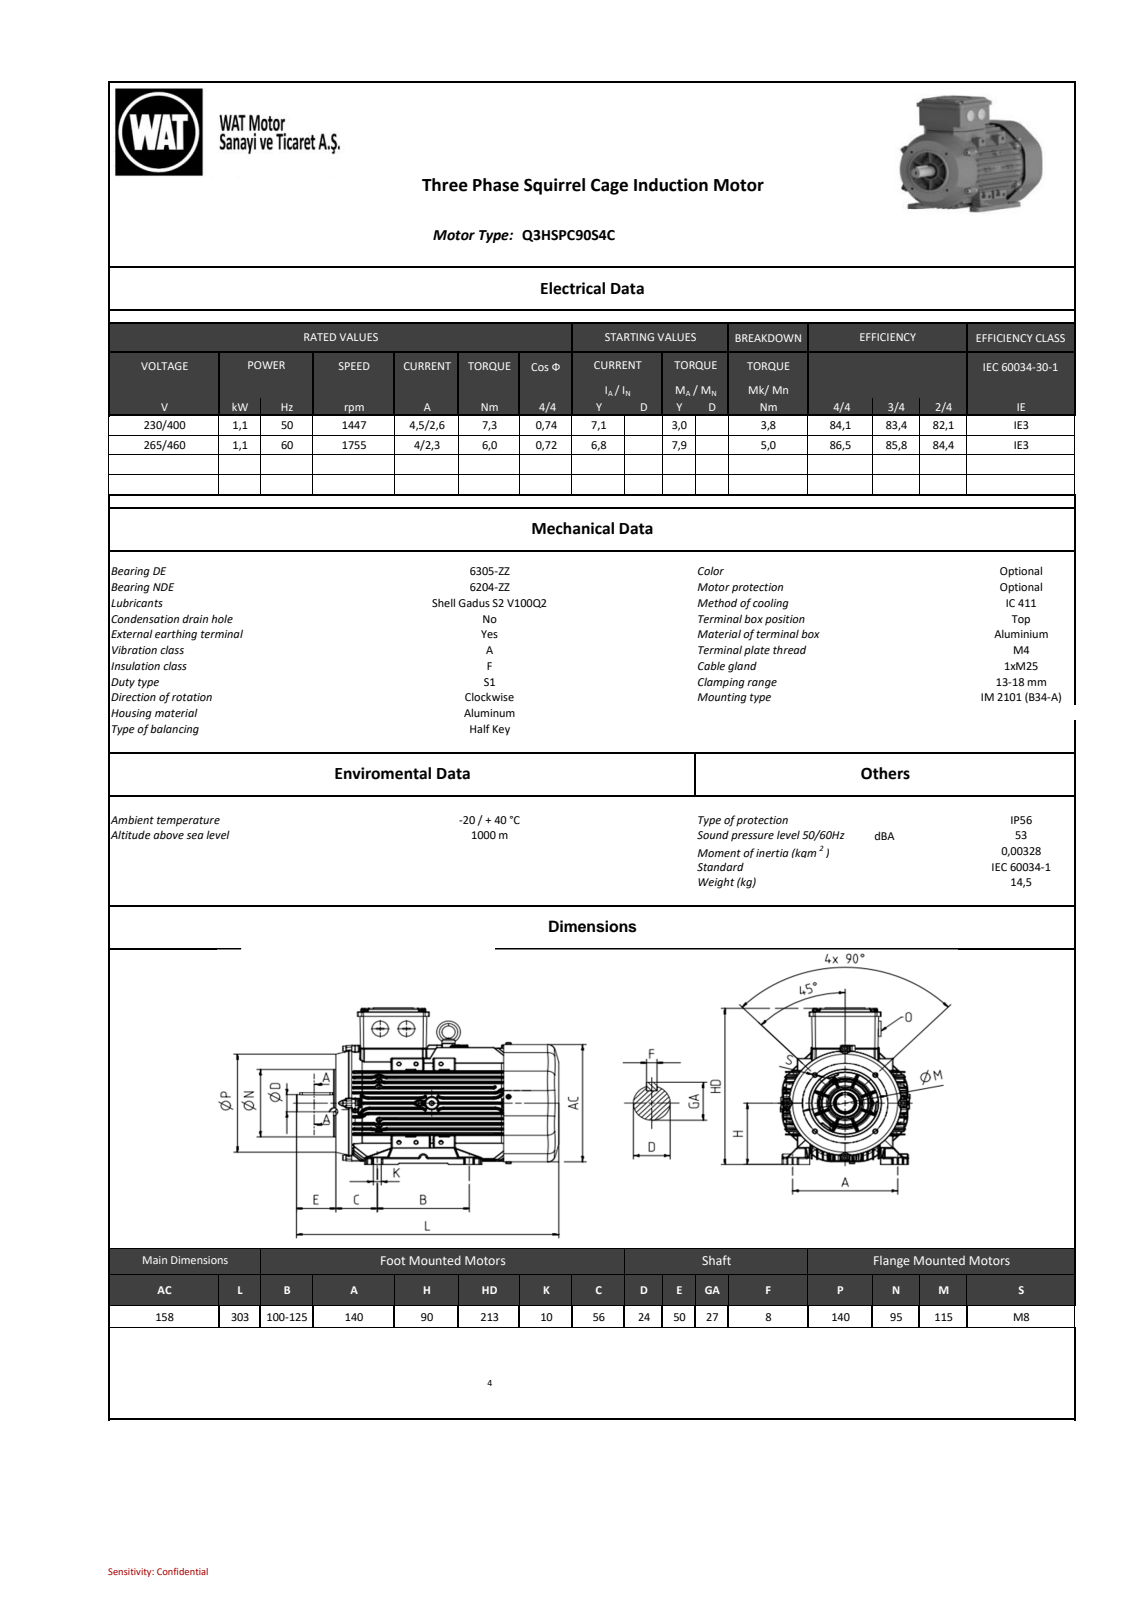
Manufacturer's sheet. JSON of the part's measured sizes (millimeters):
{"part_name": "Ar311A3C0609zsd1", "step_written_by": "SIEMENS PLM Software NX 9.0 (AUTOMOTIVE_DESIGN)", "units": "millimeters", "bodies": {"solids": 0, "faces": 8755, "planar": 1749, "cylindrical": 2795, "other": 4211}, "overall_size": [303, 211.5, 162.94], "round_holes": [[6.8, 5], [4.92, 4], [3, 3], [3.95, 3], [6.4, 3], [4.6, 2], [3.5, 1], [3.99, 1], [4.13, 1], [8, 1], [8.4, 1], [40, 1]], "round_bosses_or_shafts": [[6, 12], [11.6, 4], [10, 4], [9.3, 4], [9.2, 4], [8.33, 4], [146.5, 1], [95, 1]], "partial_cylinders_radius": [[0.5, 1256], [0.8, 341], [1, 185], [0.75, 22], [2, 21], [4, 14], [0.1, 11], [5, 11]], "face_to_face_distances": [1, 138, 6, 30.99, 4, 168.99, 39.5, 153, 40.5, 41.96], "hole_center_spacings": [25.5, 57.5, 81.32, 34.5, 39.18, 59.11, 59.76, 22.2]}
